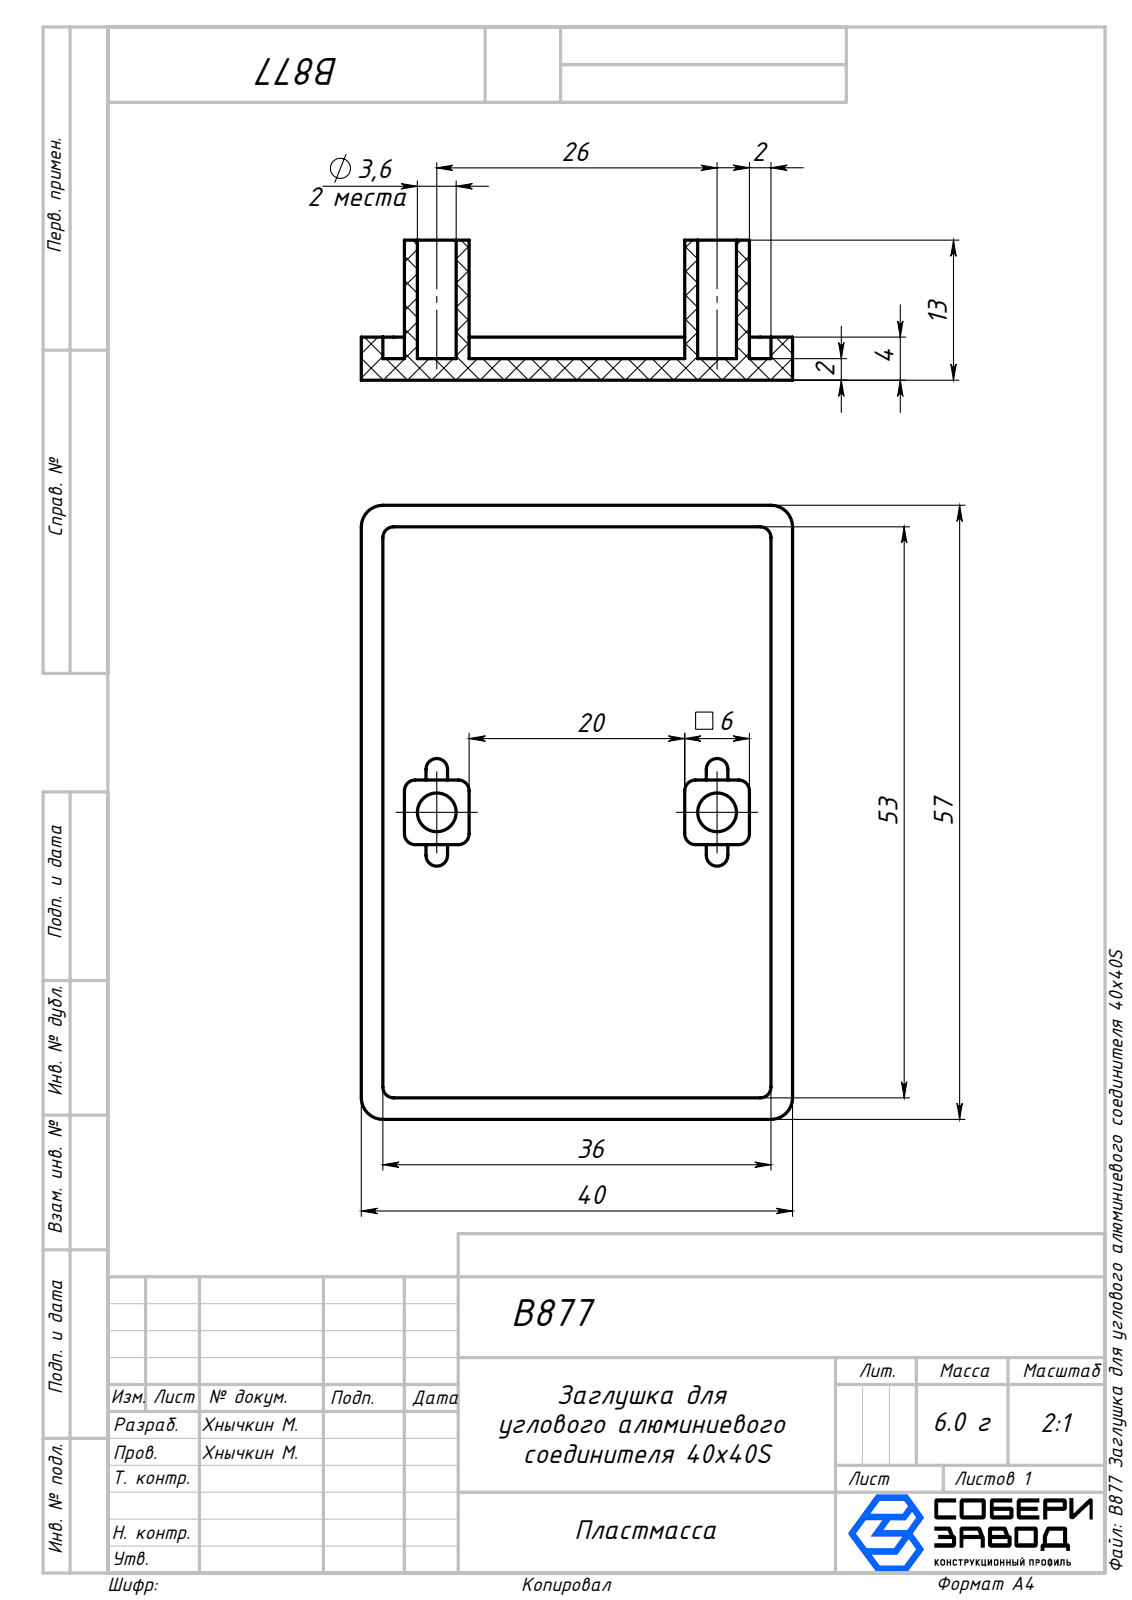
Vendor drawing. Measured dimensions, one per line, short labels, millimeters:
name: B877 Заглушка для углового алюминиевого соединителя 40х40S
written by: SolidWorks 2025 (AUTOMOTIVE_DESIGN)
unit: mm
bodies: 1 solid, 61 faces (35 planar, 26 cylindrical, 0 other)
size: 57 × 40 × 13
volume: 5 870 mm³; area: 6 432 mm²
holes: 2× ⌀3.6
rounds: 16× R1, 4× R2
face distances: 2, 4, 40, 38, 36, 6, 25.5, 31.5, 57, 55
hole spacings: 26
